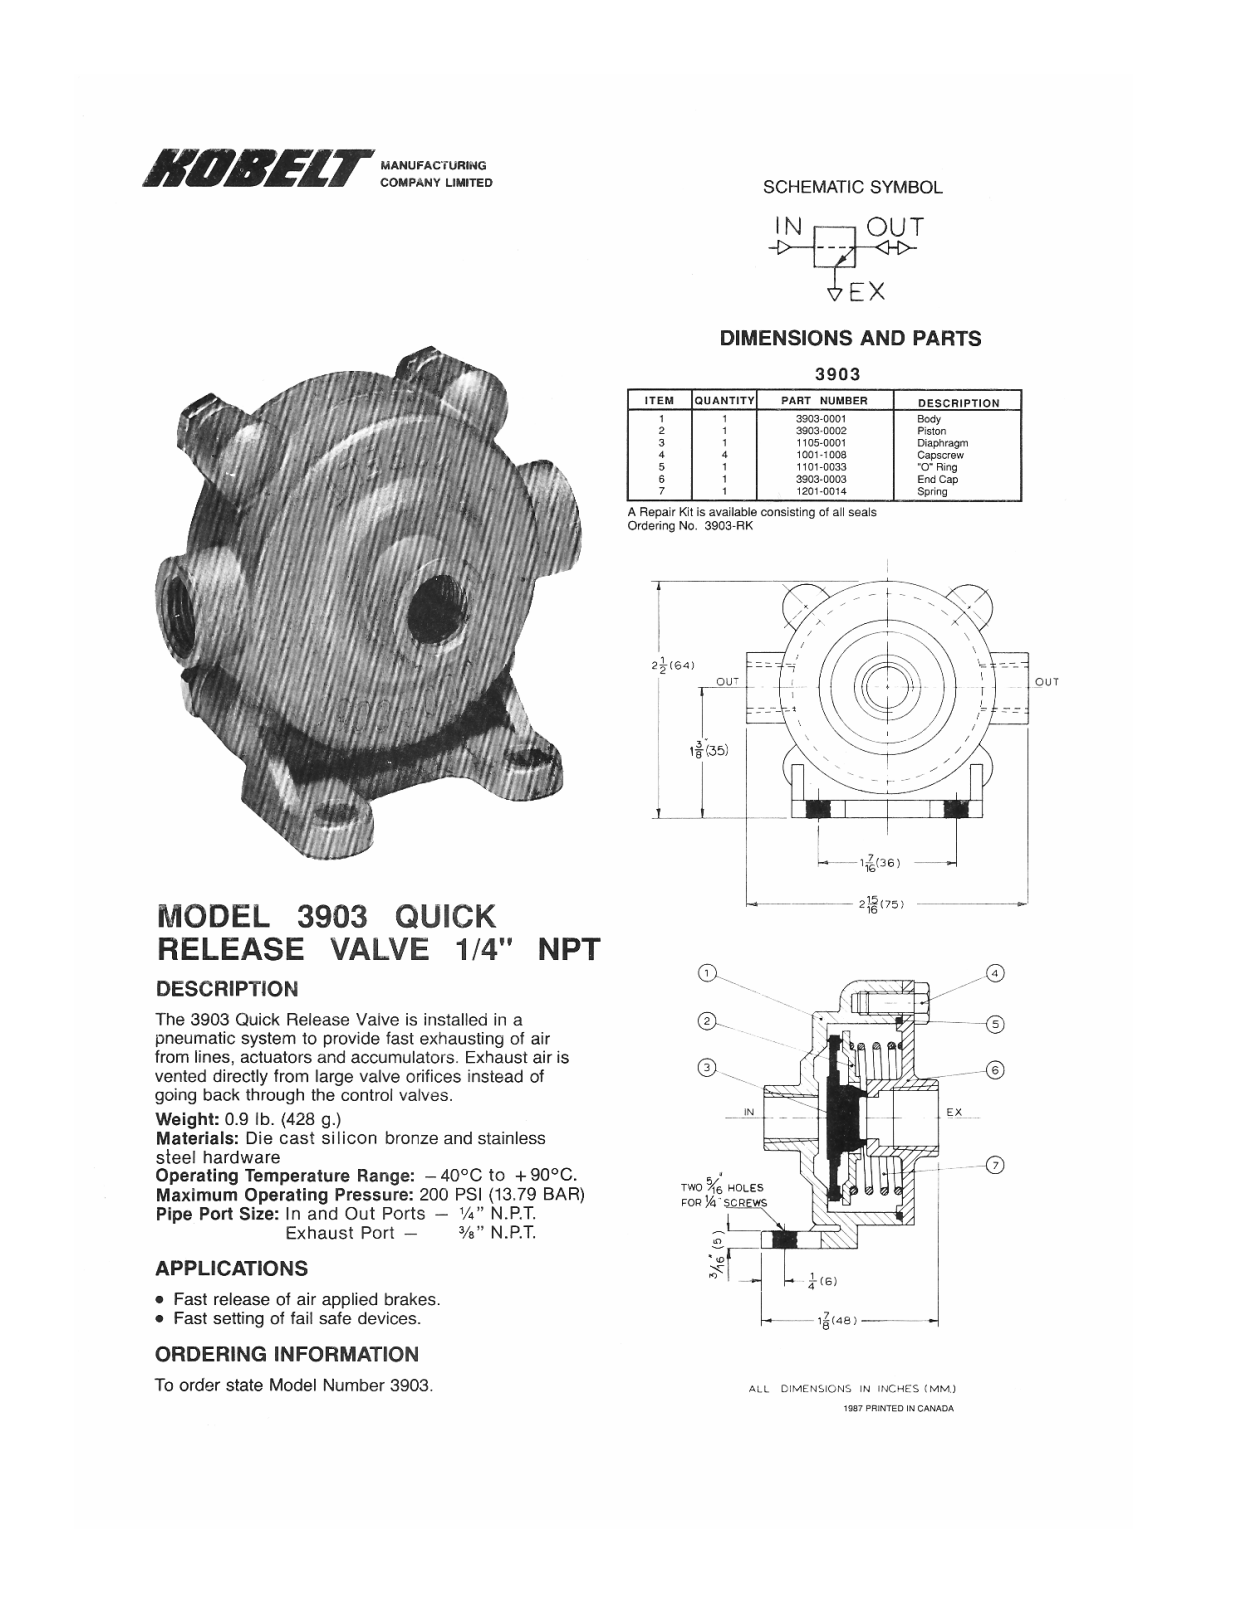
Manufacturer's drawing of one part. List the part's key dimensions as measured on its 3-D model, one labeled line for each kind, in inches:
Part name (STEP PRODUCT): 3903
STEP written by: SolidWorks 2023 (AUTOMOTIVE_DESIGN)
Units: inches
Bodies: 0 solids, 515 faces (185 planar, 79 cylindrical, 251 other)
Overall size (bounding box): 2.956 × 2.508 × 1.866
Round holes (diameter × count): ⌀0.281 ×2, ⌀0.5 ×1, ⌀0.562 ×1, ⌀2.005 ×1
Round bosses / shafts (diameter × count): ⌀0.437 ×4, ⌀2.25 ×1, ⌀0.8 ×1, ⌀0.75 ×1, ⌀0.71 ×1
Partial cylindrical surfaces — rounded edges, fillets, slot ends (radius × count): R0.031 ×11, R0.17 ×8, R0.02 ×4, R0.25 ×4, R0.281 ×2, R1.132 ×1
Main face-to-face distances: 1.04, 0.9, 0.14, 0.45, 0.188, 0.125, 0.575, 0.59, 1.196, 0.746
Hole centre spacings: 1.438
